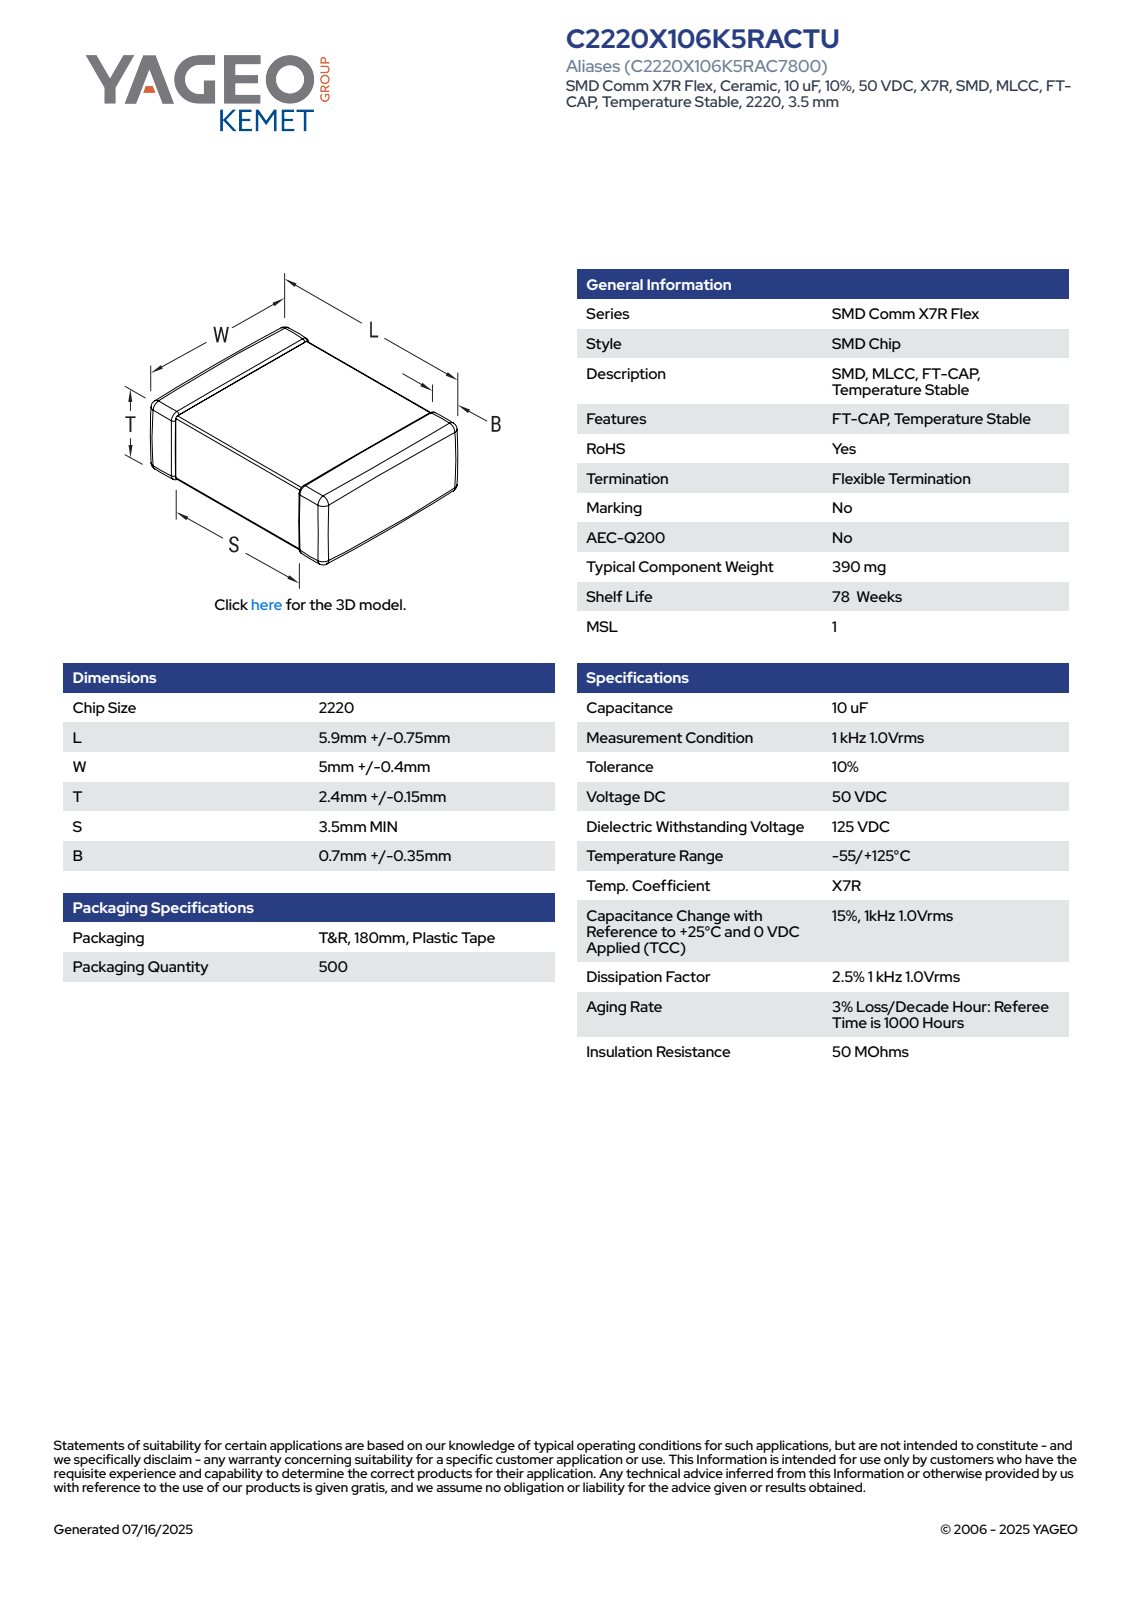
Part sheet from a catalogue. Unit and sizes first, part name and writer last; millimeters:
Units: millimetres
Overall size (bounding box): 6.65 × 5.4 × 2.55
Partial cylindrical surfaces — rounded edges, fillets, slot ends (radius × count): R0.11 ×24
Main face-to-face distances: 2.33, 2.44, 6.65, 5.18, 2.55, 5.29, 5.4, 2.8, 3.85, 3.59
Volume: 83 mm³ · Surface area: 132 mm²
Bodies: 4 solids, 121 faces (71 planar, 34 cylindrical, 16 other)
Part name (STEP PRODUCT): CCS_CCSTD_2220_L6.65W5.4T2.55B0.7
STEP written by: SolidWorks 2021 (AUTOMOTIVE_DESIGN)
